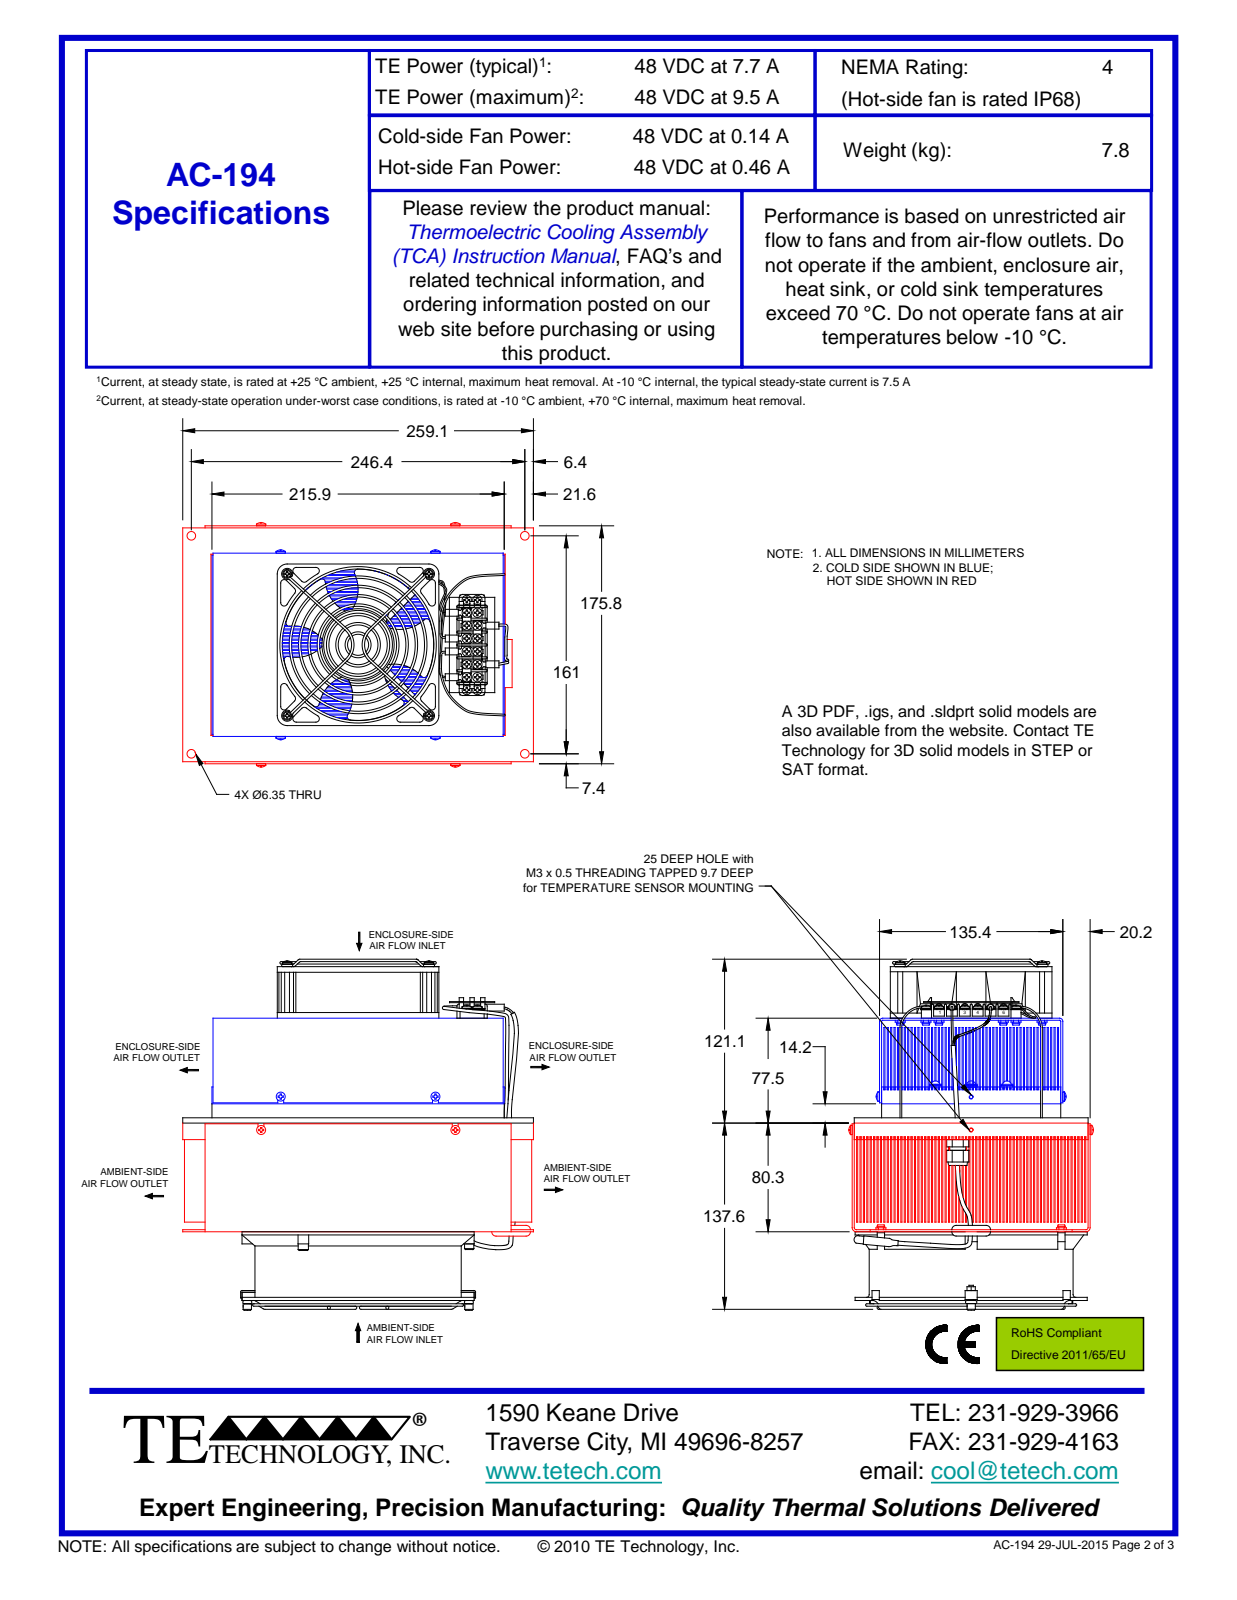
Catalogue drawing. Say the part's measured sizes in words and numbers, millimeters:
The part is named "825-3179-001 heat sink; 825-3183-001 cold sink assy; 820-2615-001; 810-3176-001 heat sink shroud (+8 more)". Its 3-D file was written by "Alibre (AUTOMOTIVE_DESIGN)". It is 195 solids with 4715 faces: 2777 planar, 827 cylindrical and 1111 other. Overall it measures 259.08 by 257.42 by 180.8 millimeters. Its volume is 3 320 000 cubic millimeters and its surface area 3 719 000 square millimeters. Round holes: 25 of diameter 2.64, 11 of diameter 2.65, 11 of diameter 5.56, 10 of diameter 4.22, 10 of diameter 6.35, 6 of diameter 1.91, 6 of diameter 3.53, 6 of diameter 3.94, 6 of diameter 4.17, 6 of diameter 4.27, 6 of diameter 4.32, 6 of diameter 4.78. Round bosses or shafts: 34 of diameter 3.51, 22 of diameter 6.86, 16 of diameter 2.3, 13 of diameter 5.74, 12 of diameter 1.68, 12 of diameter 1.4, 11 of diameter 6.34, 10 of diameter 1.42. Partial cylindrical surfaces (rounded edges, fillets, slot ends): 44 of radius 1, 29 of radius 0.5, 24 of radius 0.79, 21 of radius 0.95, 12 of radius 0.78, 12 of radius 0.81, 12 of radius 2, 8 of radius 0.38. The main face-to-face distances are 5.03, 10.06, 2.51, 7.54, 12.57, 15.09, 17.6, 2.52, 22.63, 20.12. The hole center spacings are 68.11, 81.02, 52.84, 91.27, 19.05, 58.49, 70.73, 78.4.
